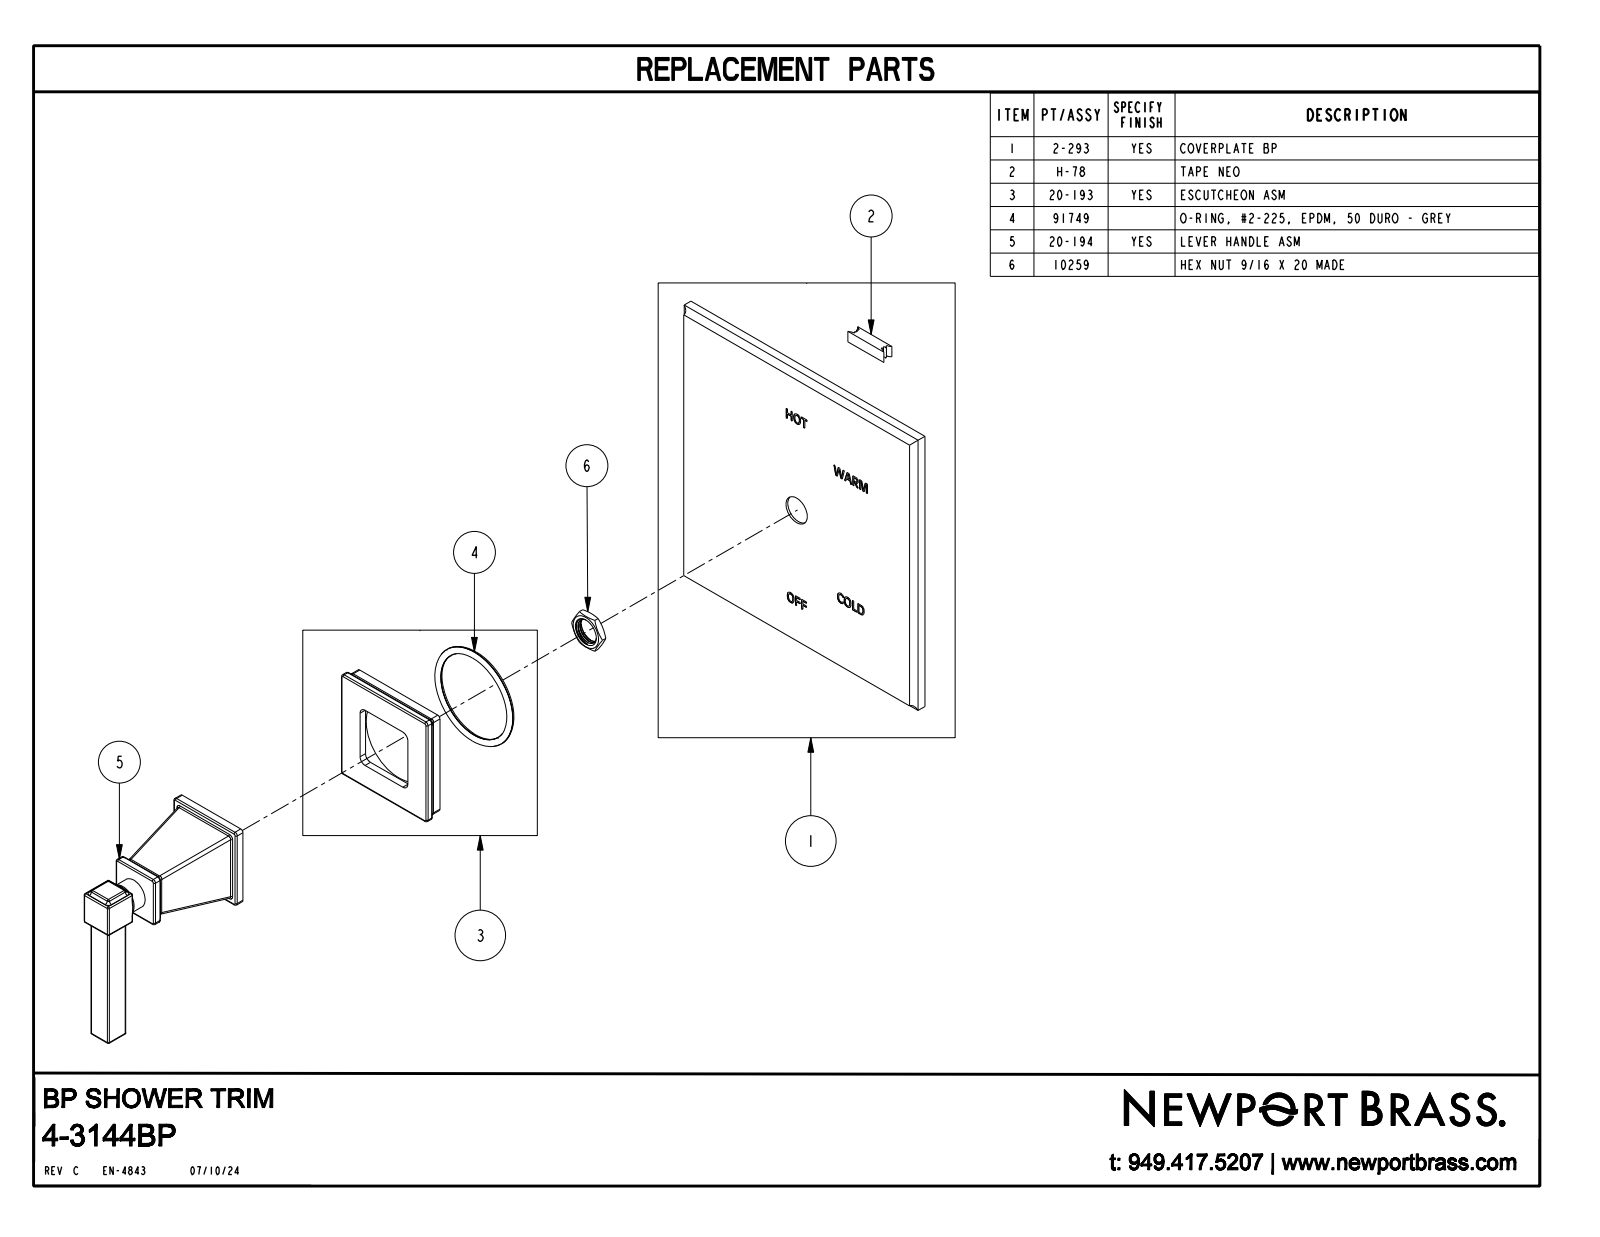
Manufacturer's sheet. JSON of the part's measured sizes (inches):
{"part_name": "4-3144BP", "step_written_by": "CREO PARAMETRIC BY PTC INC, 2018400 (CONFIG_CONTROL_DESIGN)", "units": "inches", "bodies": {"solids": 1, "faces": 447, "planar": 171, "cylindrical": 100, "other": 176}, "overall_size": [6.5, 6.5, 3.941], "volume_in3": 19.63, "surface_area_in2": 114.8, "round_bosses_or_shafts": [[0.625, 1], [0.506, 1]], "partial_cylinders_radius": [[0.03, 48], [0.06, 28], [0.09, 8], [0.125, 4], [0.23, 4]], "face_to_face_distances": [0.313, 0.723, 0.41, 6.5, 0.5, 3, 3.5, 2.105, 4.395, 0.593]}
